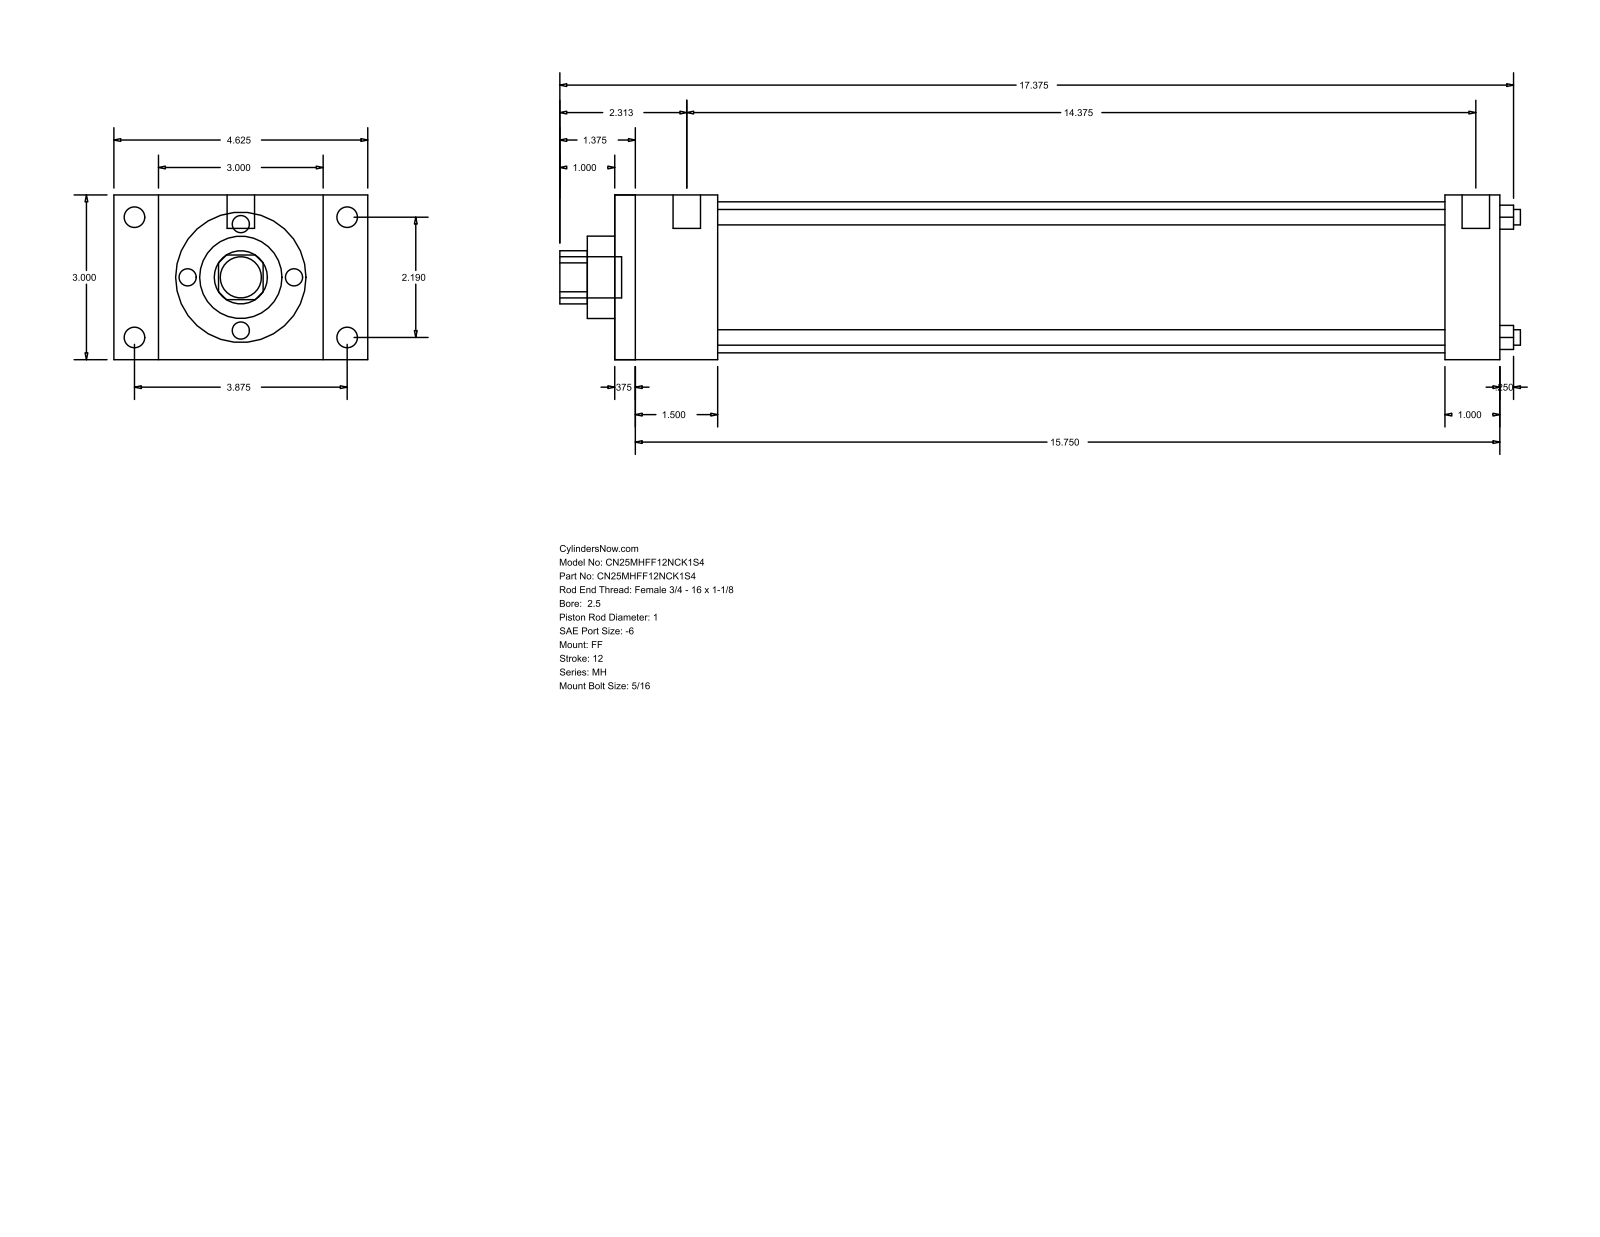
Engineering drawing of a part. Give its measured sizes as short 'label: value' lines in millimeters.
name: MH_FF__0250_1
written by: GSSL Pune (CONFIG_CONTROL_DESIGN)
unit: mm
bodies: 0 solids, 92 faces (64 planar, 28 cylindrical, 0 other)
size: 444.5 × 117.47 × 76.2
holes: 4× ⌀7.14, 1× ⌀25.4, 1× ⌀38.1, 1× ⌀69.85
bosses: 4× ⌀9.53, 4× ⌀5.56, 2× ⌀12.7, 1× ⌀19.05
rounds: 1× R12.29
face distances: 76.2, 409.58, 9.52, 400.06, 47.63, 384.17, 38.11, 374.65, 336.54, 361.95
hole spacings: 39.33, 55.62, 78.66
